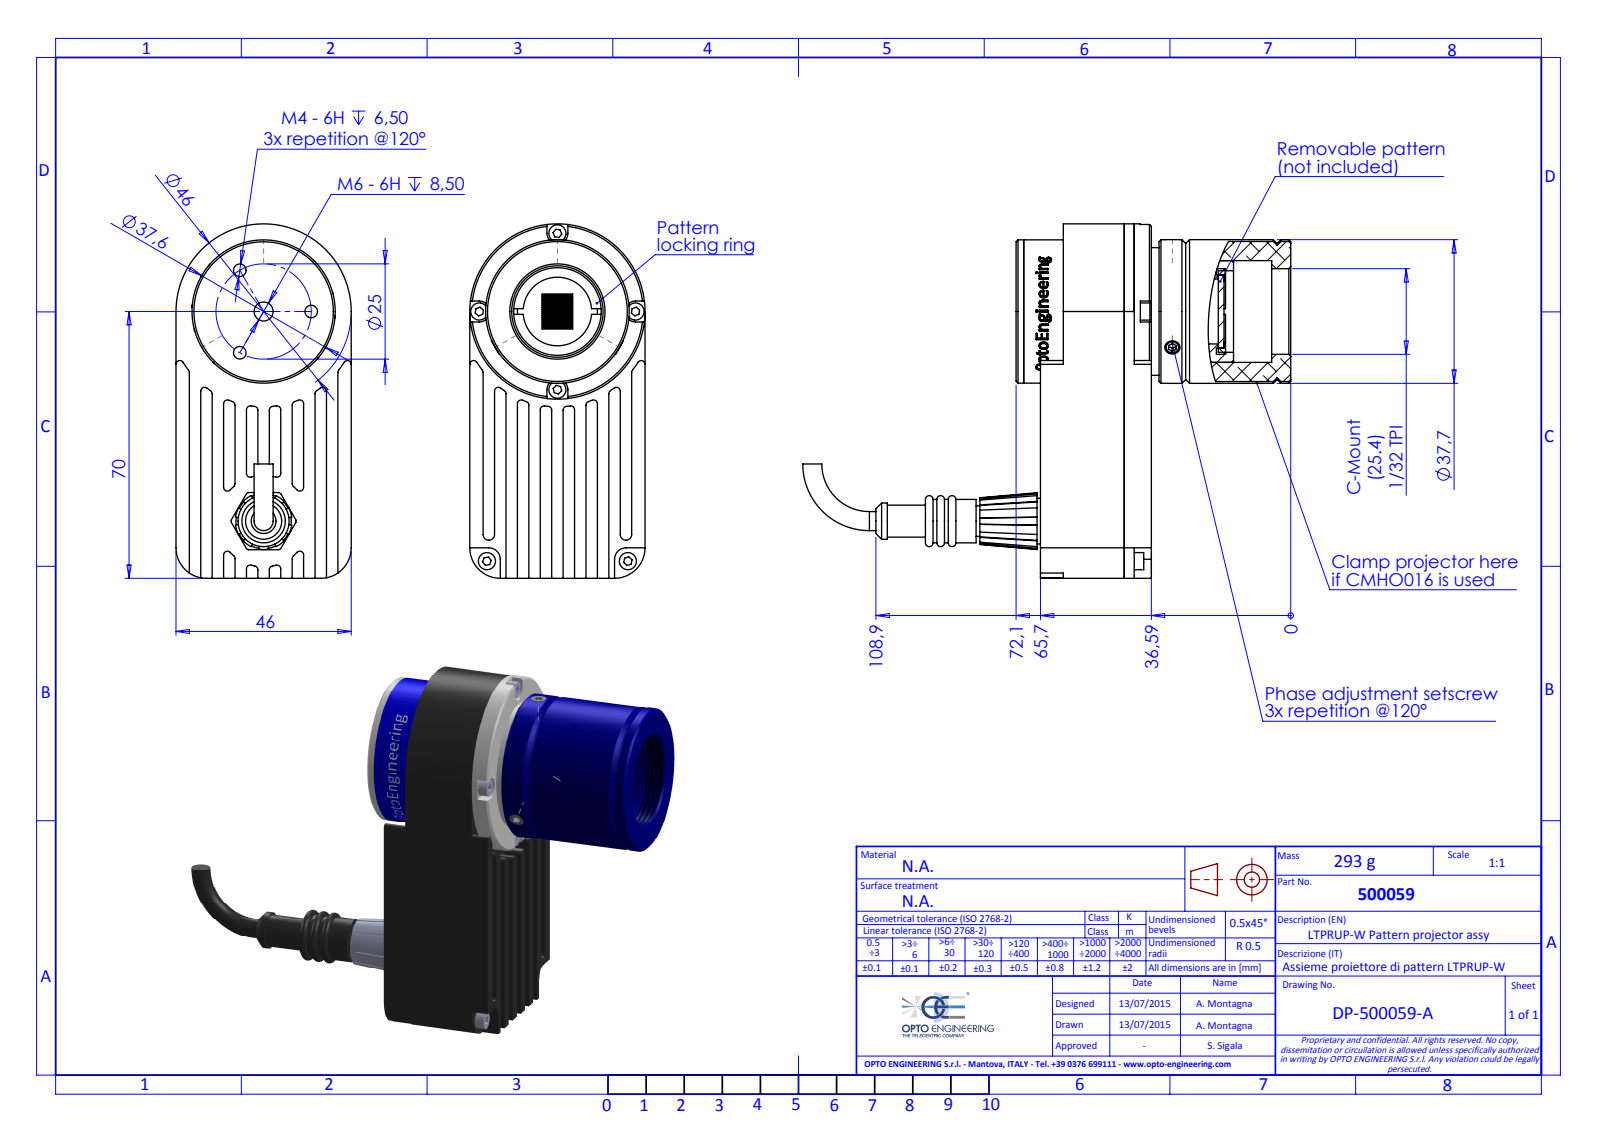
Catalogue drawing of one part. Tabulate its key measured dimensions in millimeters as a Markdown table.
| quantity | value |
| --- | --- |
| part name | LTPRUP |
| STEP written by | SolidWorks 2014 (AUTOMOTIVE_DESIGN) |
| units | millimeters |
| bodies | 0 solids, 1614 faces (625 planar, 490 cylindrical, 499 other) |
| overall size | 128.1 × 93 × 46 |
| round holes (diameter × count) | 2.05 × 8, 2.5 × 6, 2.9 × 6, 3.3 × 6, 3.4 × 6, 1.2 × 4, 6.5 × 4, 1.7 × 3, 1.6 × 2, 2.64 × 2, 3.1 × 2, 1.3 × 1 |
| round bosses / shafts (diameter × count) | 4.5 × 6, 2.4 × 6, 1 × 4, 0.8 × 4, 4 × 3, 46 × 1, 37.7 × 1, 37.6 × 1 |
| partial cylindrical surfaces (radius × count) | 1 × 33, 0.81 × 10, 4 × 10, 0.5 × 6, 0.2 × 5, 0.85 × 4, 1.02 × 4, 1.26 × 4 |
| main face-to-face distances | 6, 15, 3, 9, 21, 12, 18.61, 4.5, 18, 1.5 |
| hole center spacings | 12.5, 24.01, 8, 11.51, 15.4, 17.68, 17.9, 20.5 |
